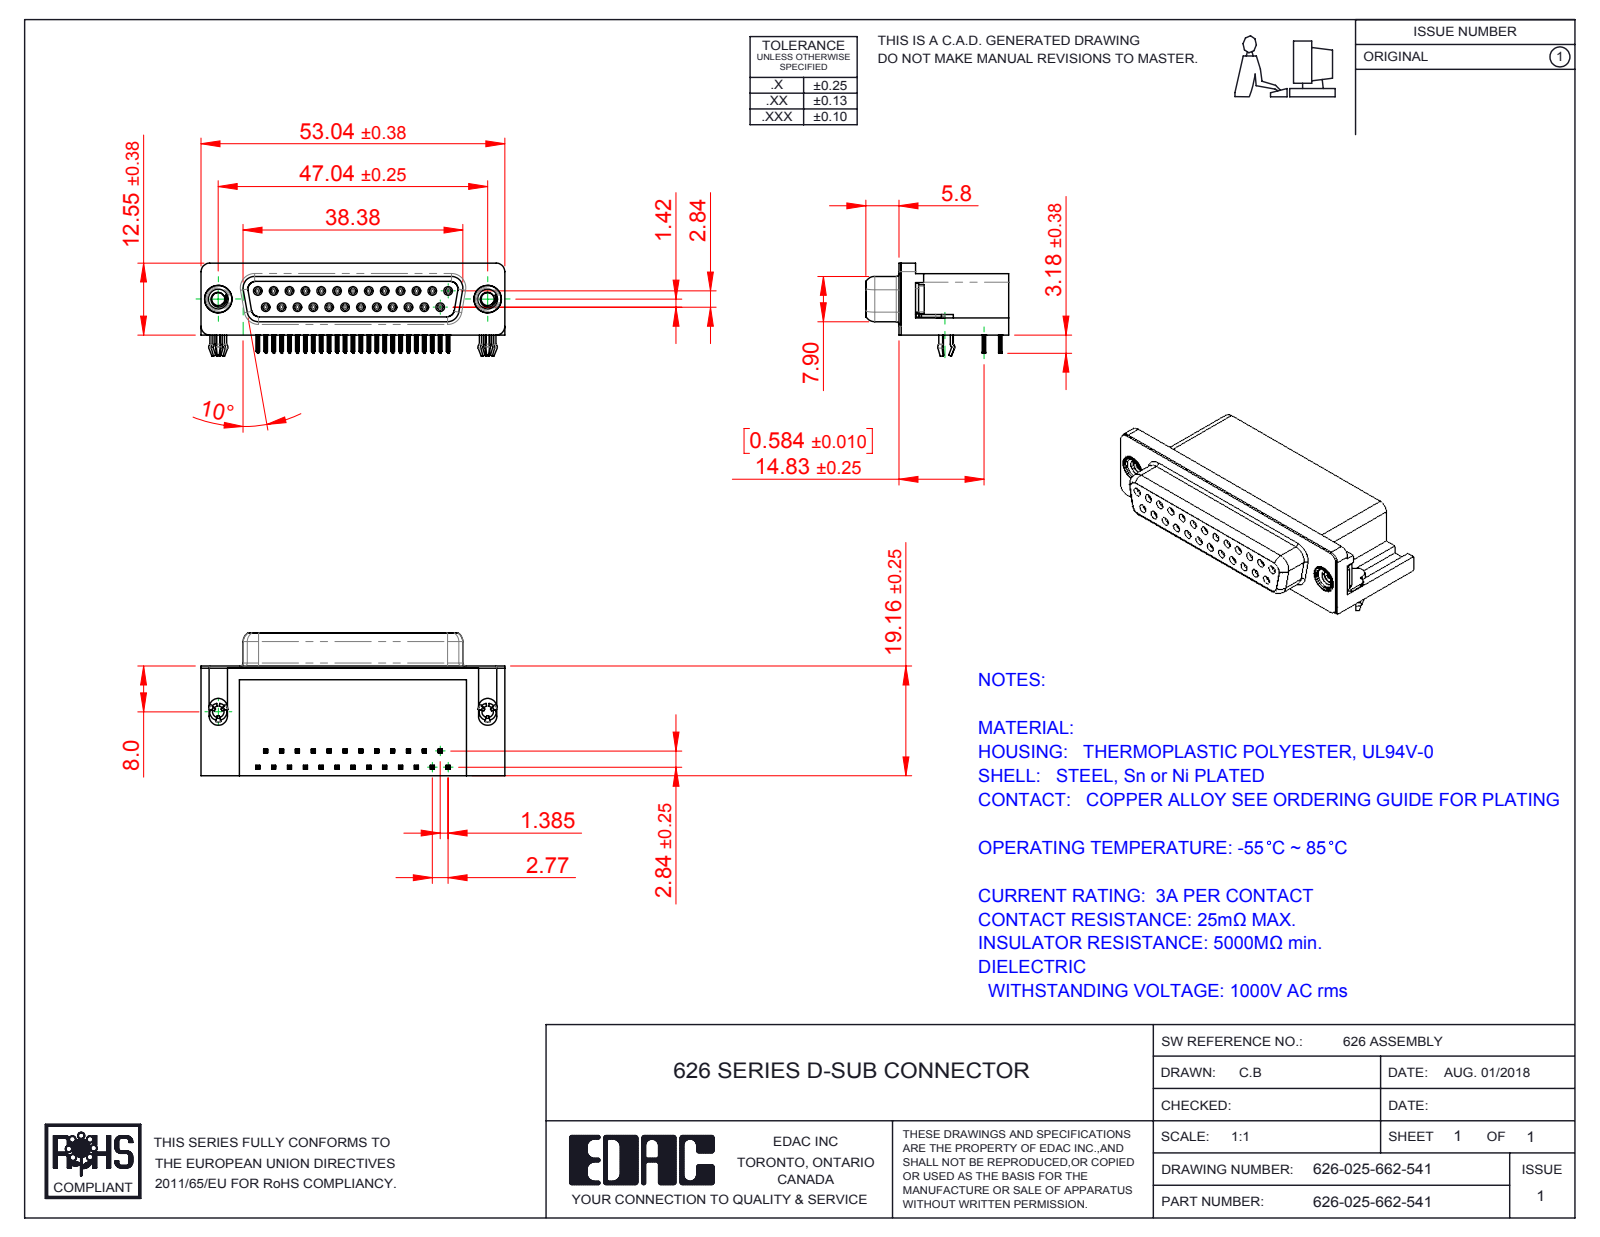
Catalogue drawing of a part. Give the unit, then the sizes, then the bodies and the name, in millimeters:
Units: millimetres
Overall size (bounding box): 53.04 × 24.96 × 16.25
Round holes (diameter × count): ⌀0.8 ×25, ⌀0.9 ×25, ⌀2 ×2, ⌀2.26 ×2, ⌀4 ×2, ⌀4.8 ×2, ⌀5 ×2
Round bosses / shafts (diameter × count): ⌀1.2 ×25, ⌀4.9 ×2, ⌀4.75 ×2, ⌀3.9 ×2, ⌀3 ×2
Partial cylindrical surfaces — rounded edges, fillets, slot ends (radius × count): R0.1 ×200, R0.15 ×100, R0.35 ×50, R0.34 ×25, R1 ×18, R0.25 ×12, R0.28 ×12, R1.35 ×8
Main face-to-face distances: 0.4, 10.35, 18.76, 6.2, 2.73, 9.38, 3.18, 0.85, 2.84, 0.35
Hole centre spacings: 3.16, 2.77, 5.54, 8.31, 11.08, 5.03, 5.04, 7.48
Volume: 10 680 mm³ · Surface area: 11 426 mm²
Bodies: 31 solids, 3954 faces (1760 planar, 926 cylindrical, 1268 other)
Part name (STEP PRODUCT): 626-025-662-541; 626 4-40 Threaded Rivet; 626 3 Prong Board Lock; 626 Contact Top (+3 more)
STEP written by: SolidWorks 2016 (CONFIG_CONTROL_DESIGN)
